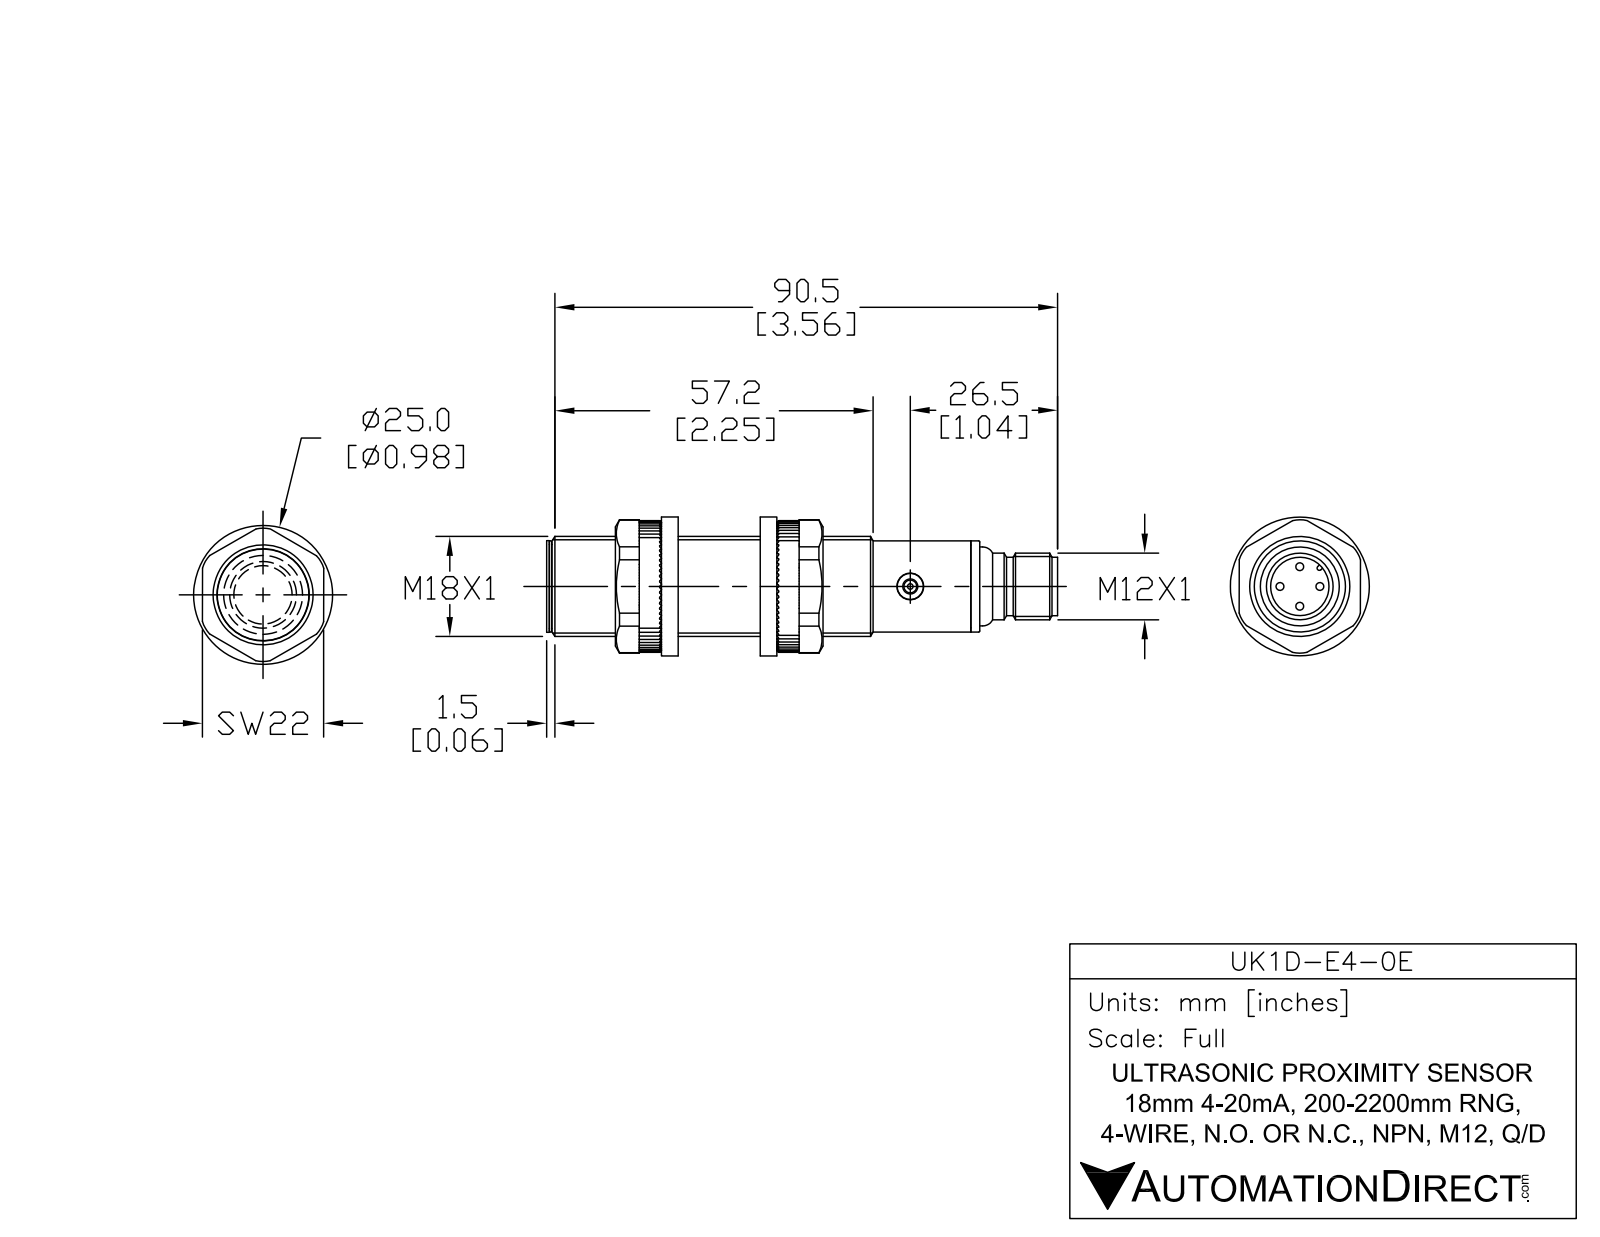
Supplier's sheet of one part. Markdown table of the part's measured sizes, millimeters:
| quantity | value |
| --- | --- |
| part name | UK1D-E4-0E |
| STEP written by | SolidWorks 2017 (AUTOMOTIVE_DESIGN) |
| units | millimeters |
| bodies | 6 solids, 106 faces (21 planar, 48 cylindrical, 37 other) |
| overall size | 91.6 × 18 × 18 |
| volume | 19 700 mm³ |
| surface area | 6 890 mm² |
| round holes (diameter × count) | 2.7 × 1, 4.7 × 1, 7 × 1, 8.3 × 1, 9.5 × 1 |
| round bosses / shafts (diameter × count) | 1 × 4, 18 × 1, 16.6 × 1, 16.4 × 1, 15.8 × 1, 14.2 × 1, 12 × 1, 10.5 × 1 |
| partial cylindrical surfaces (radius × count) | 0.6 × 1 |
| main face-to-face distances | 75.1, 1, 76.1, 0.9, 76, 1.1, 4, 77.6, 77.5, 76.6 |
